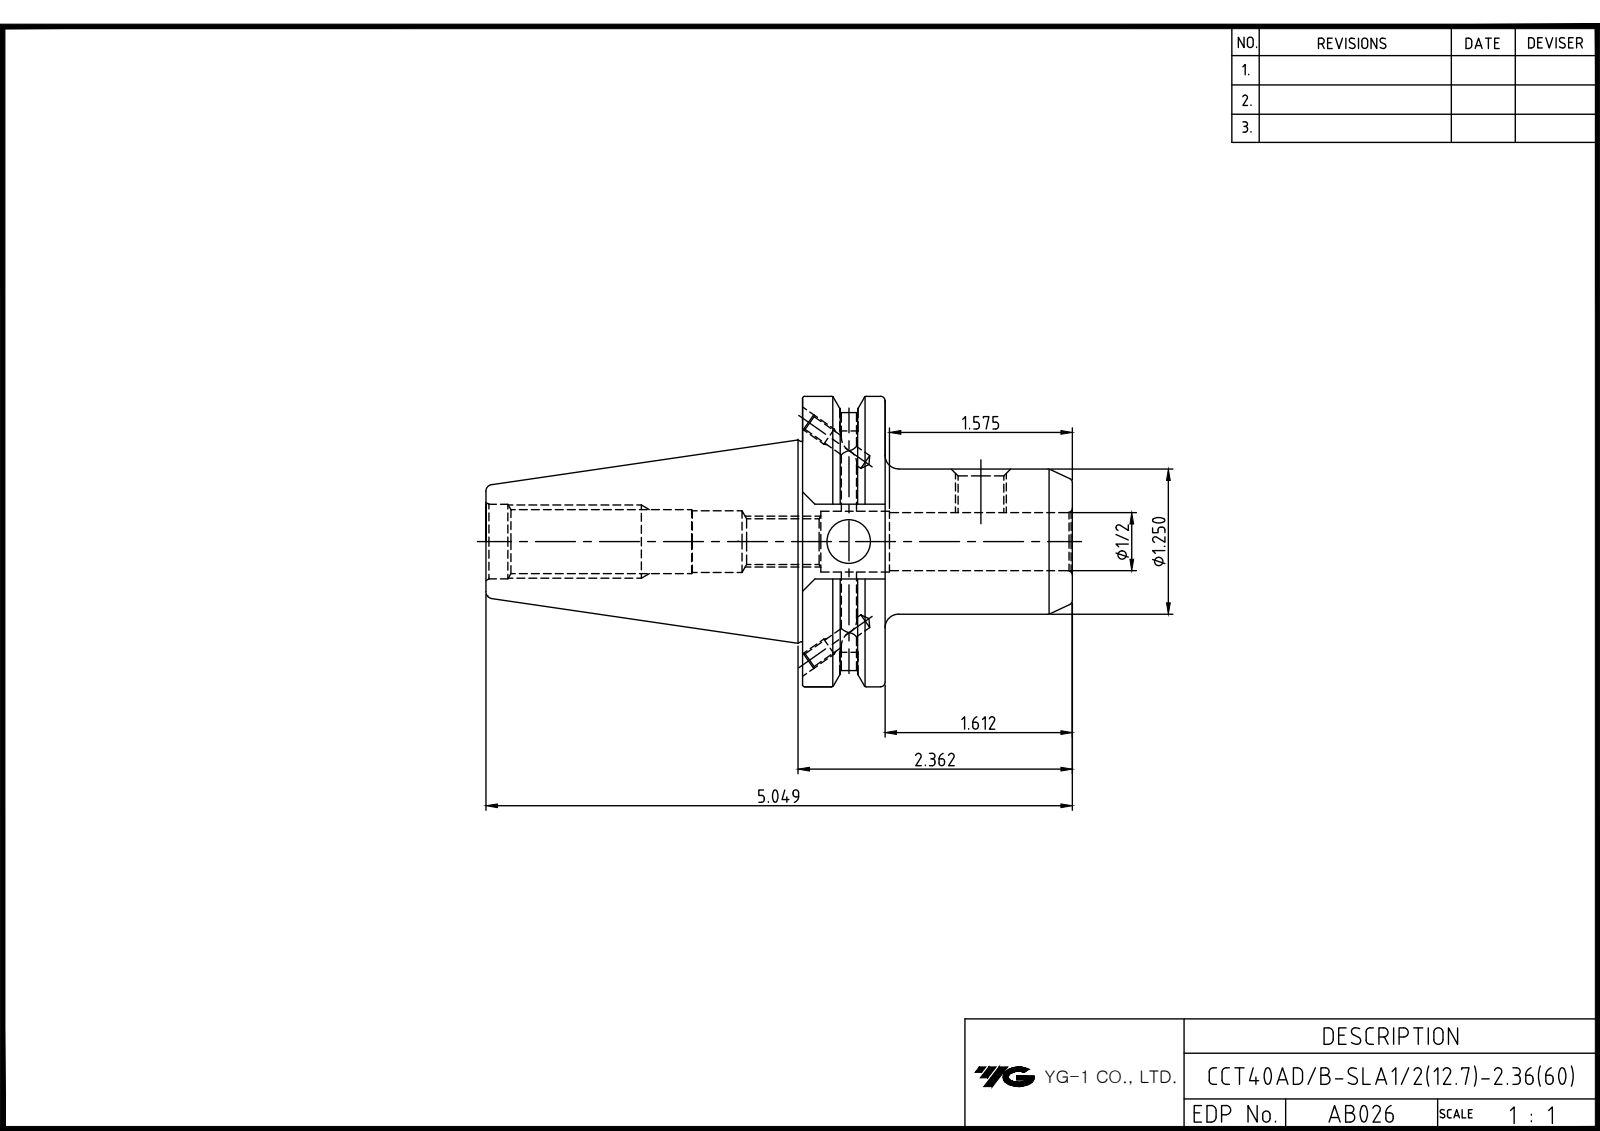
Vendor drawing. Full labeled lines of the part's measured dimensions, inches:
Part name (STEP PRODUCT): LO-CCT40ADB-SLA12.7-60
STEP written by: Autodesk Inventor 2025 (AUTOMOTIVE_DESIGN)
Units: inches
Bodies: 1 solid, 92 faces (39 planar, 29 cylindrical, 24 other)
Overall size (bounding box): 5.049 × 2.5 × 2.405
Volume: 7.968 in³ · Surface area: 40.97 in²
Round holes (diameter × count): ⌀0.128 ×4, ⌀0.157 ×2, ⌀0.165 ×2, ⌀0.37 ×1, ⌀0.375 ×1, ⌀0.383 ×1, ⌀0.5 ×1, ⌀0.527 ×1, ⌀0.547 ×1, ⌀0.642 ×1
Round bosses / shafts (diameter × count): ⌀2.5 ×1, ⌀1.724 ×1, ⌀1.25 ×1
Partial cylindrical surfaces — rounded edges, fillets, slot ends (radius × count): R1.108 ×1
Main face-to-face distances: 0.711, 2.323, 1.612, 1.874, 0.645, 2.726, 3.437, 5.049, 3.2, 0.474
